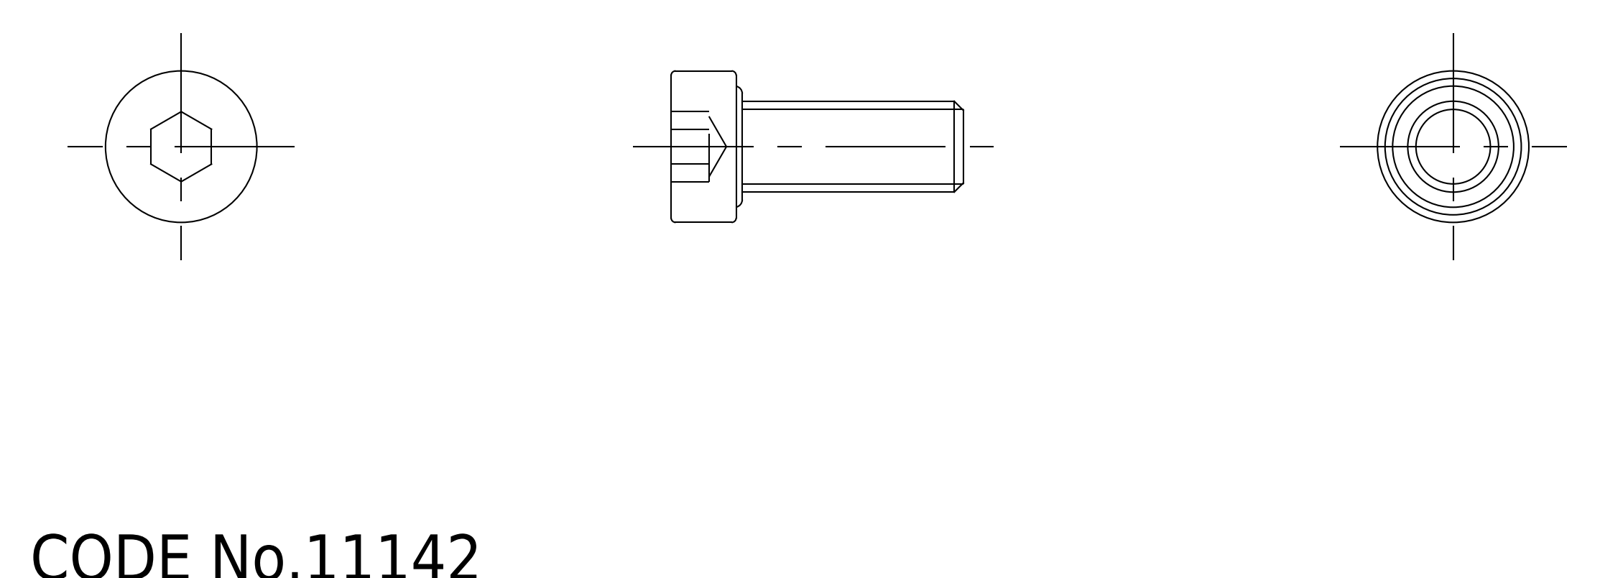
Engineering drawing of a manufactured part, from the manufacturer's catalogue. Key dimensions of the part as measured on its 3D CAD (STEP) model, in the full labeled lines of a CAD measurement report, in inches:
Part name (STEP PRODUCT): TL_418_M6_15; screw
STEP written by: SolidWorks 2015 (AUTOMOTIVE_DESIGN)
Units: inches
Bodies: 2 solids, 27 faces (11 planar, 6 cylindrical, 10 other)
Overall size (bounding box): 0.76 × 0.394 × 0.394
Volume: 0.044 in³ · Surface area: 1.07 in²
Round holes (diameter × count): ⌀0.354 ×1
Round bosses / shafts (diameter × count): ⌀0.394 ×1, ⌀0.236 ×1
Main face-to-face distances: 0.146, 0.76, 0.614, 0.157, 0.098, 0.047, 0.661, 0.169, 0.071, 0.024
